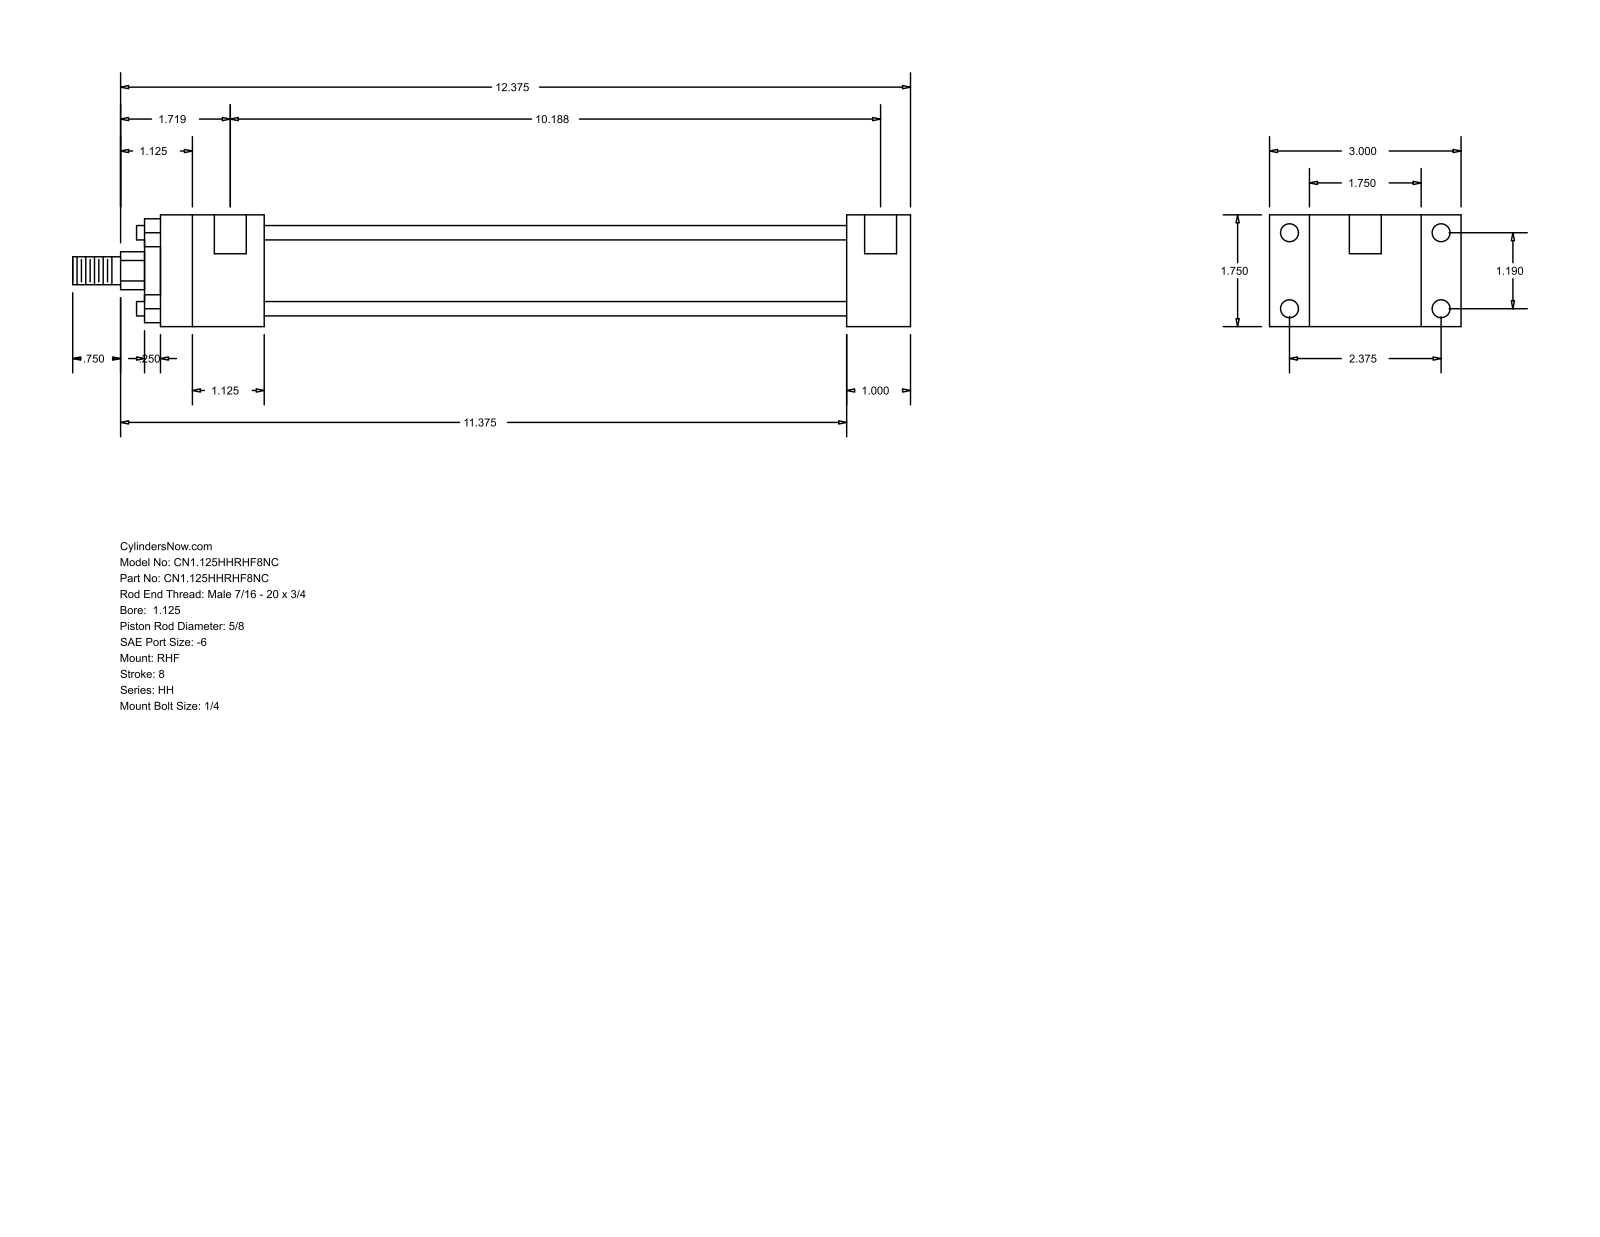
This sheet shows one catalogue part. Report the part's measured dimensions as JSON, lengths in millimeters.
{"part_name": "HH_RHF__0112_0.625", "step_written_by": "GSSL Pune (CONFIG_CONTROL_DESIGN)", "units": "millimeters", "bodies": {"solids": 0, "faces": 88, "planar": 60, "cylindrical": 28, "other": 0}, "overall_size": [333.38, 76.2, 44.45], "round_holes": [[5.56, 4], [7.14, 4], [12.7, 2]], "round_bosses_or_shafts": [[5.71, 4], [34.92, 1], [28.57, 1], [15.88, 1], [11.11, 1]], "partial_cylinders_radius": [[7.54, 1]], "face_to_face_distances": [44.46, 15.87, 60.33, 25.39, 76.2, 231.78, 257.17, 41.27, 273.05, 298.44], "hole_center_spacings": [30.22, 60.32, 67.47, 255.59, 3.17, 258.76]}
